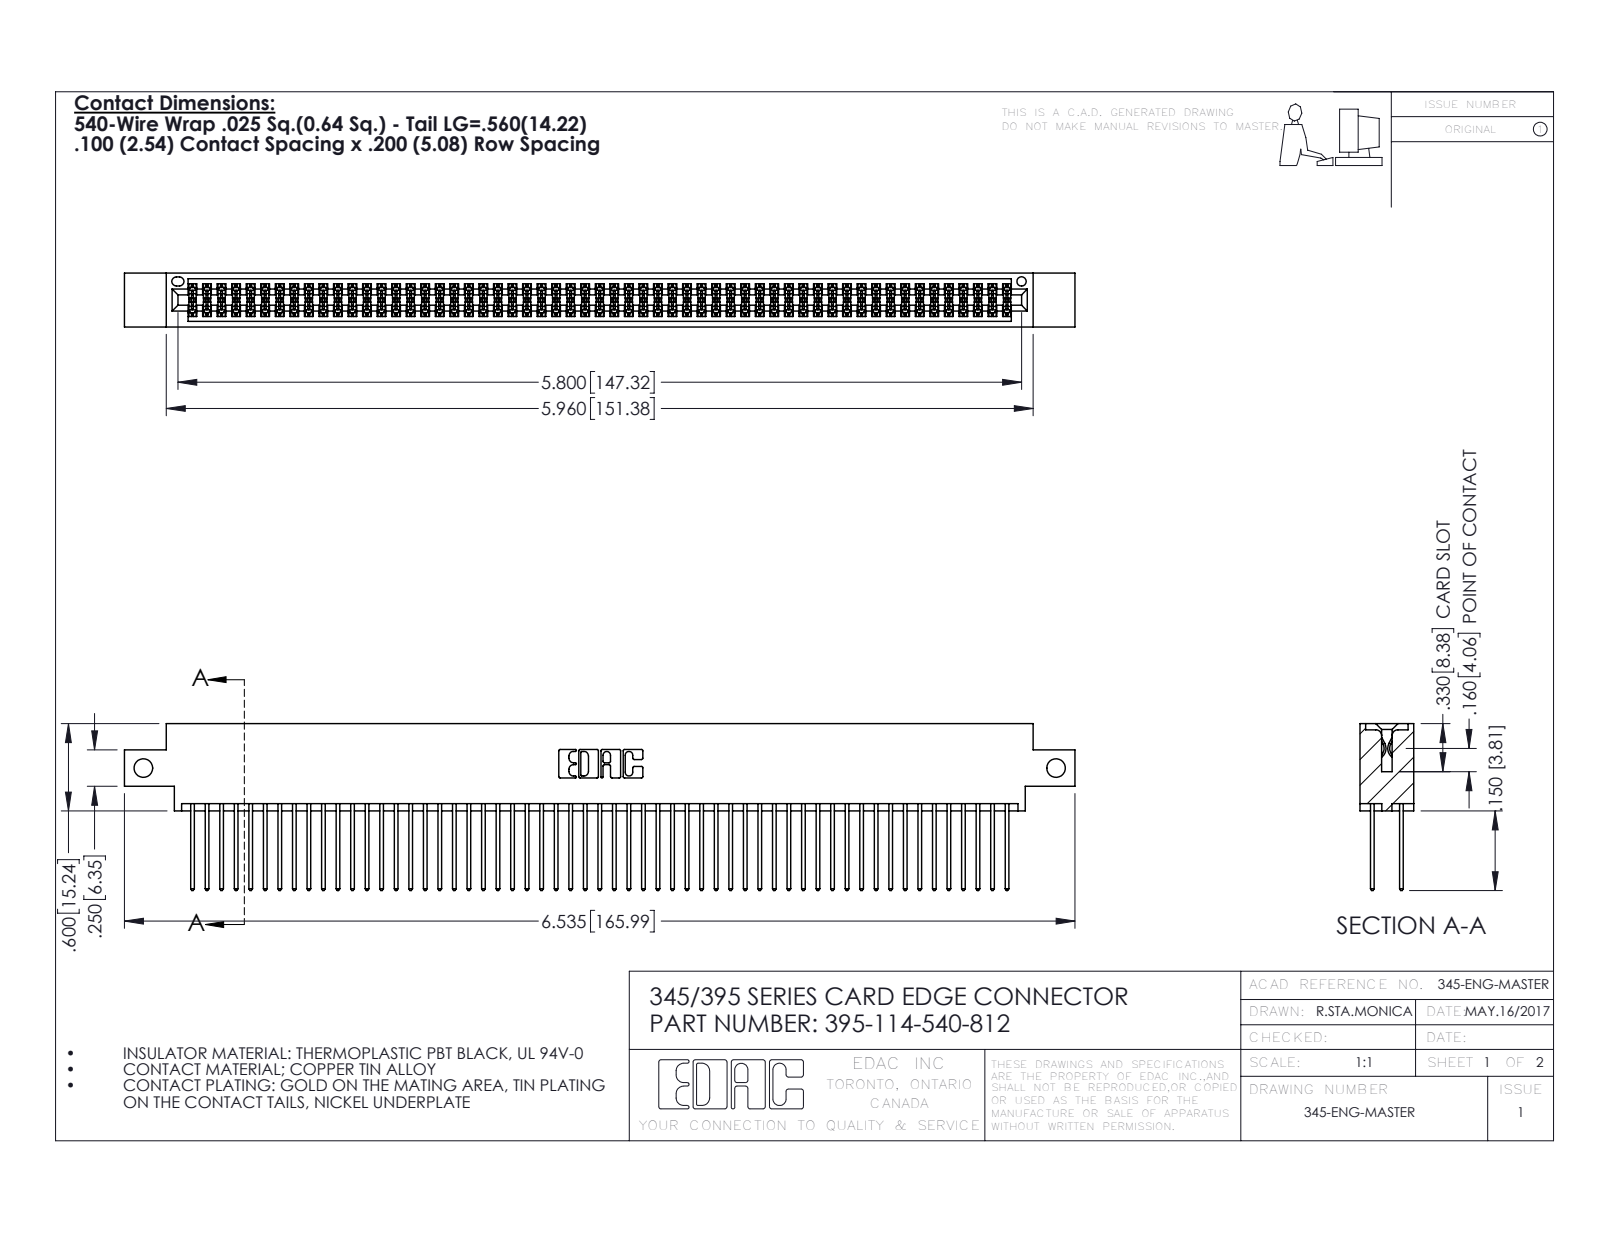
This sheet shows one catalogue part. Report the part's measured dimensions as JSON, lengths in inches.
{"part_name": "345 Part_0.170 Offset - Side Mount; 395-114-540-812; 345-292-001_345-293-140", "step_written_by": "SolidWorks 2016 (CONFIG_CONTROL_DESIGN)", "units": "inches", "bodies": {"solids": 115, "faces": 5830, "planar": 3846, "cylindrical": 1984, "other": 0}, "overall_size": [6.535, 1.147, 0.37], "volume_in3": 1.007, "surface_area_in2": 41.36, "round_holes": [[0.128, 2], [0.064, 1]], "partial_cylinders_radius": [[0.006, 171], [0.01, 114], [0.01, 22], [0.007, 6], [0.031, 6], [0.026, 3], [0.014, 2], [0.019, 2]], "face_to_face_distances": [0.072, 0.298, 0.2, 0.098, 0.272, 0.025, 0.37, 0.225, 0.175, 0.149], "hole_center_spacings": [6.275]}
